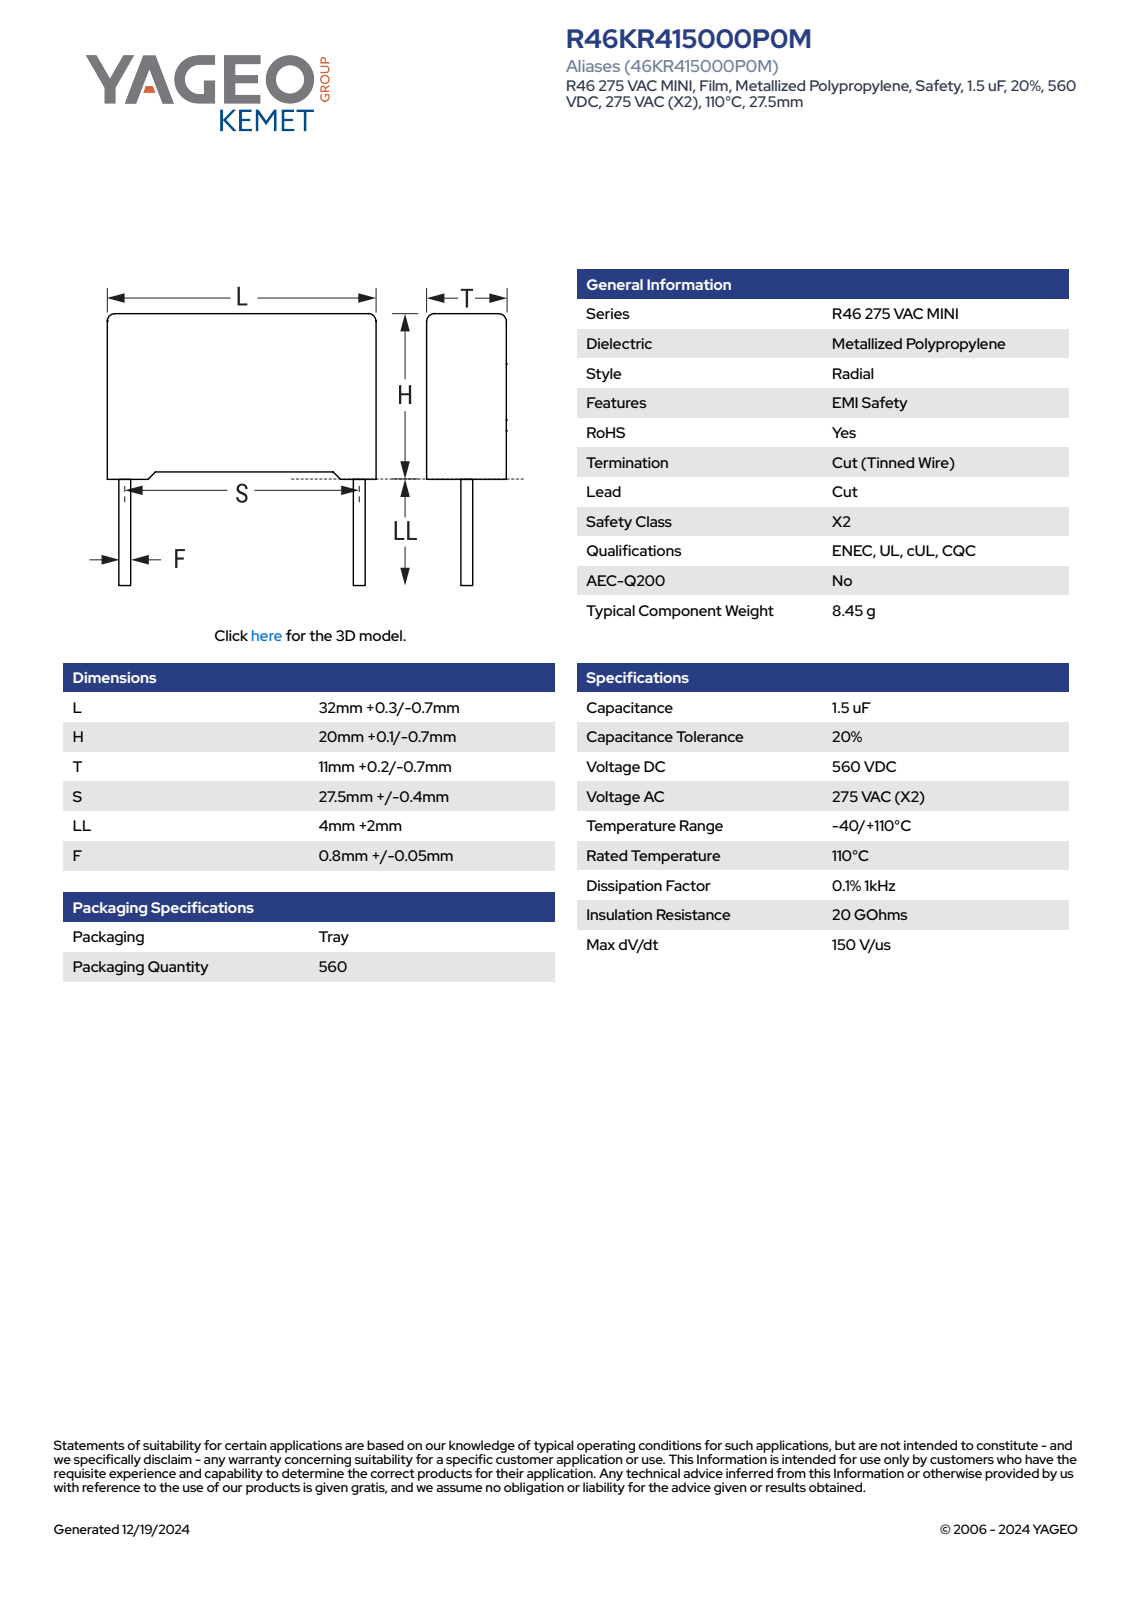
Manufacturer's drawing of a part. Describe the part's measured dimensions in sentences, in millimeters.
The part is named "CFR_RB2_32X20X11_L32.3H20.1T11.2S27.5LL6F0.85". Its 3-D file was written by "SolidWorks 2021 (AUTOMOTIVE_DESIGN)". It is 4 solids with 85 faces: 77 planar, 8 cylindrical and 0 other. Overall it measures 32.3 by 26.1 by 11.21 millimeters. Its volume is 7 035 cubic millimeters and its surface area 2 562 square millimeters. Round bosses or shafts: 2 of diameter 0.85. Partial cylindrical surfaces (rounded edges, fillets, slot ends): 4 of radius 0.5. The main face-to-face distances are 11.2, 19.35, 32.3, 19.41, 0.69, 0.75, 20.1, 1.08, 11.21, 31.22.
